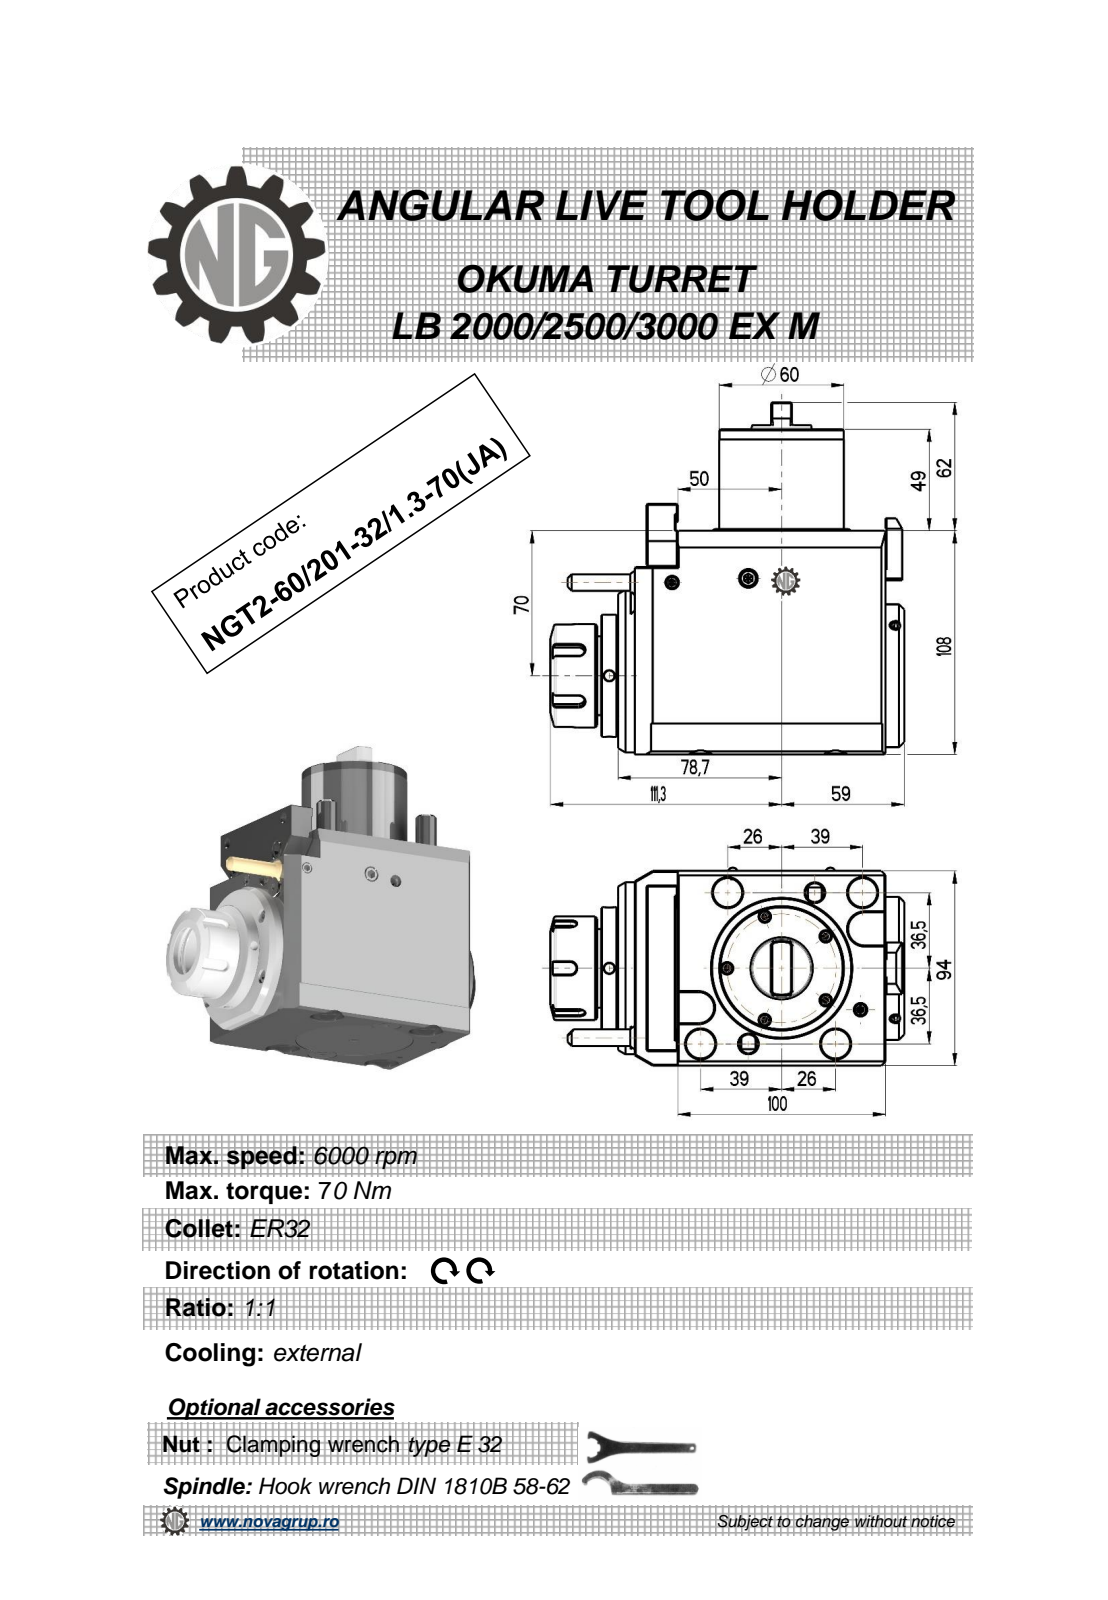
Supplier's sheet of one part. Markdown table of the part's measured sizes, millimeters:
| quantity | value |
| --- | --- |
| part name | NGT2_60_201_32_1_3_70_JA |
| STEP written by | PRO/ENGINEER BY PARAMETRIC TECHNOLOGY CORPORATION, 2010280 (CONFIG_CONTROL_DESIGN) |
| units | millimeters |
| bodies | 1 solid, 385 faces (181 planar, 98 cylindrical, 106 other) |
| overall size | 170.3 × 170 × 94 |
| volume | 1 502 000 mm³ |
| surface area | 100 373 mm² |
| round holes (diameter × count) | 5 × 5, 9 × 2, 3 × 1, 27 × 1 |
| round bosses / shafts (diameter × count) | 12 × 4, 6 × 3, 83 × 1, 69 × 1, 60 × 1, 50 × 1, 48 × 1, 41.5 × 1 |
| partial cylindrical surfaces (radius × count) | 0.31 × 10, 0.22 × 6, 0.8 × 6, 3 × 6, 7.5 × 1, 8 × 1, 13.25 × 1, 39.48 × 1 |
| main face-to-face distances | 94, 108, 128.7, 8, 9, 137.7, 129.7, 49, 120.7, 157 |
| hole center spacings | 83.38, 32.04, 56.1, 64, 72.9, 76.25, 79.71, 105.47 |
